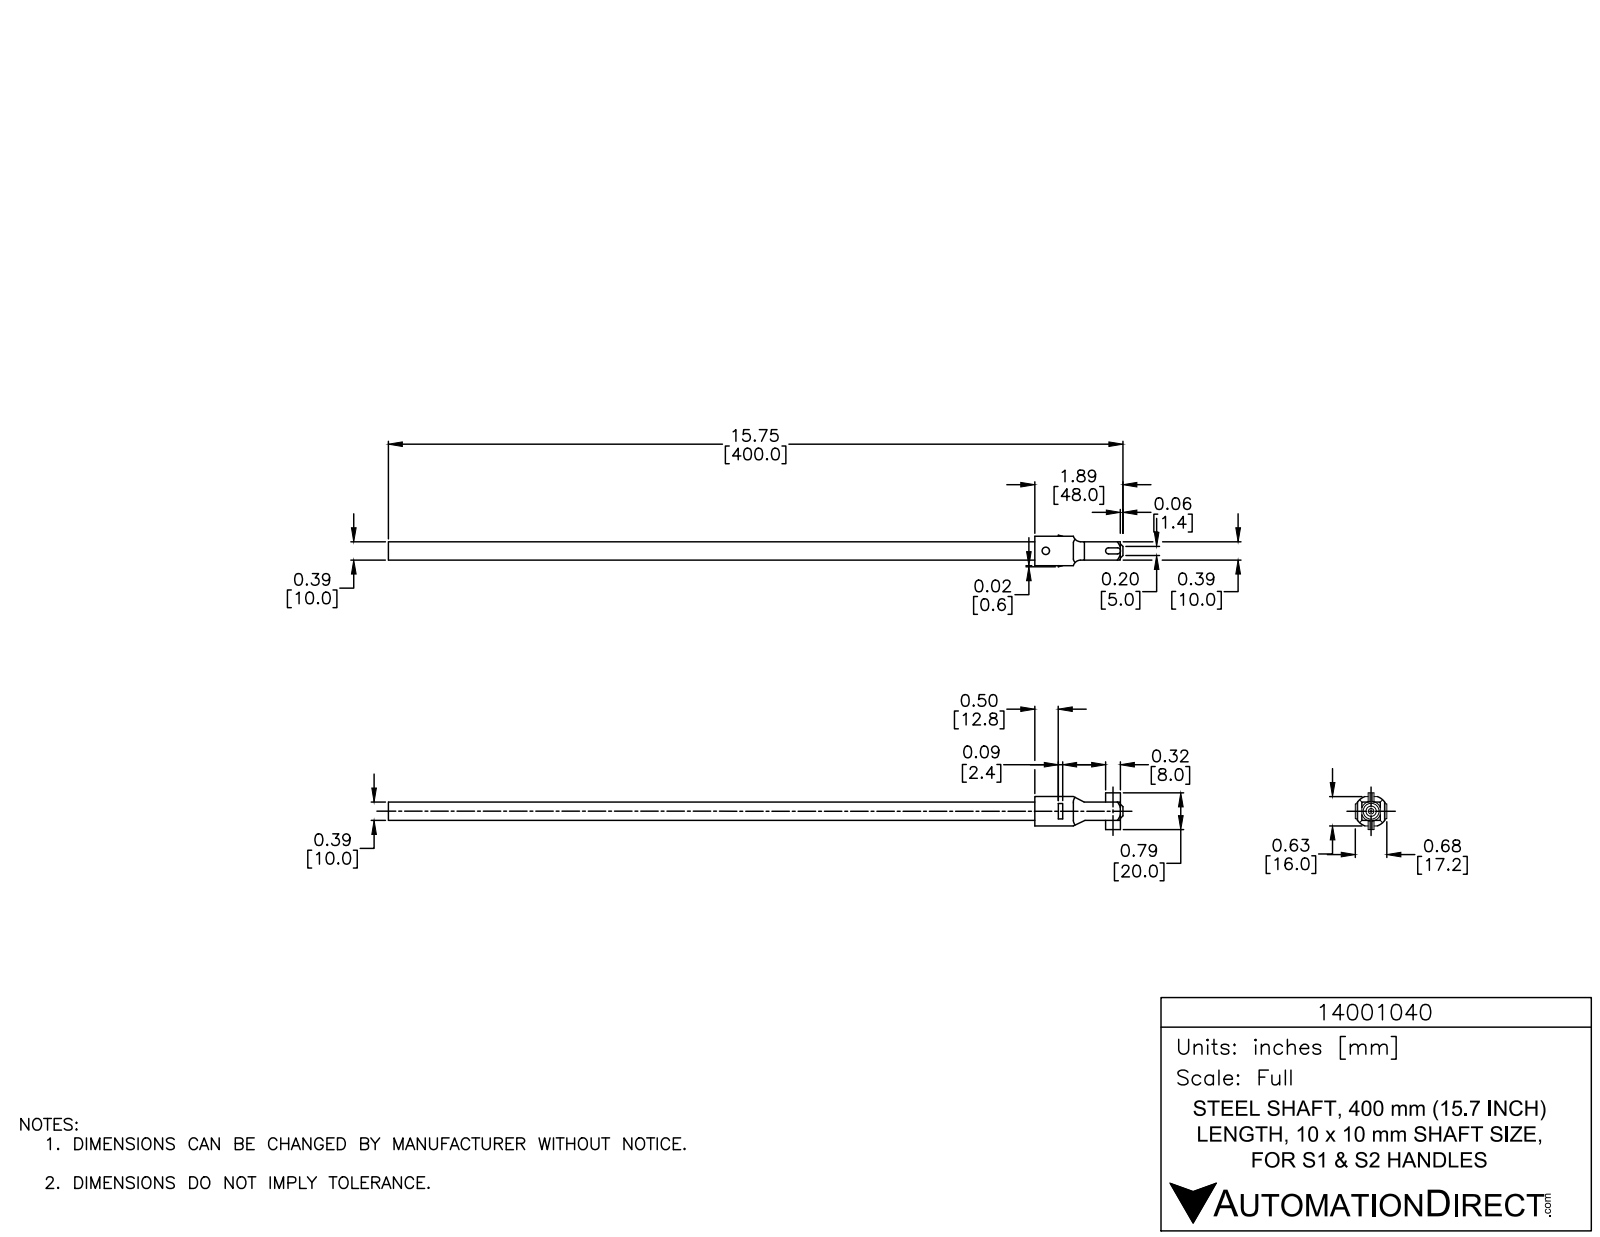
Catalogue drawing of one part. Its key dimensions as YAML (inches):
part_name: "14001040"
step_written_by: "SolidWorks 2015 (AUTOMOTIVE_DESIGN)"
units: inches
bodies: {solids: 1, faces: 72, planar: 35, cylindrical: 24, other: 13}
overall_size: [15.748, 0.787, 0.677]
volume: 2.496
surface_area: 23.93
round_bosses_or_shafts:
  - {diameter: 0.118, count: 1}
partial_cylinders:
  - {radius: 0.012, count: 4}
  - {radius: 0.118, count: 4}
  - {radius: 0.039, count: 2}
  - {radius: 0.335, count: 2}
  - {radius: 0.063, count: 1}
  - {radius: 0.236, count: 1}
face_to_face_distances: [0.394, 0.102, 0.496, 0.512, 0.118, 0.598, 0.63, 0.236, 0.362, 0.134]
